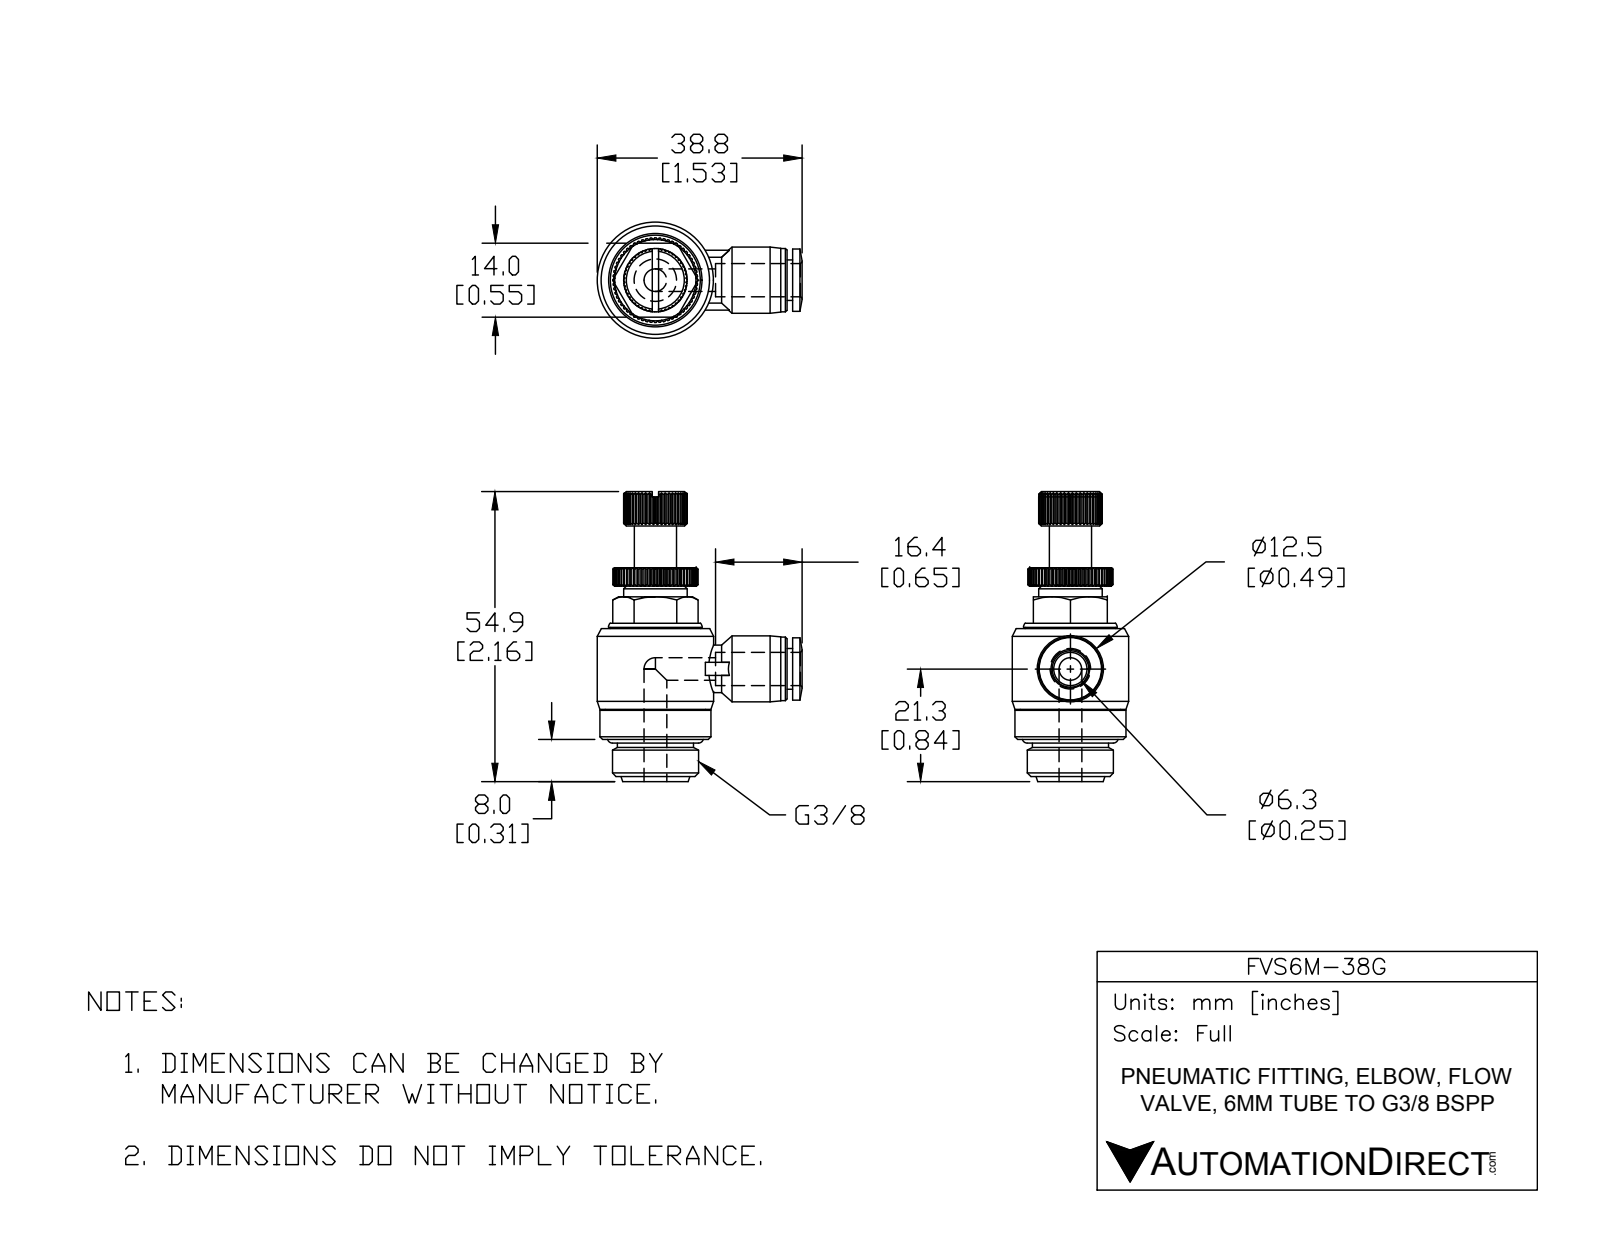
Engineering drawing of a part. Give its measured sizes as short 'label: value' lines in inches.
name: FVS6M-38G
written by: SolidWorks 2015 (AUTOMOTIVE_DESIGN)
unit: in
bodies: 2 solids, 567 faces (251 planar, 143 cylindrical, 173 other)
size: 2.161 × 1.526 × 0.866
volume: 0.802 in³; area: 9.254 in²
holes: 2× ⌀0.169, 1× ⌀0.248
bosses: 2× ⌀0.472, 1× ⌀0.866, 1× ⌀0.827, 1× ⌀0.748, 1× ⌀0.675, 1× ⌀0.642, 1× ⌀0.567, 1× ⌀0.492
rounds: 1× R0.315
face distances: 1.142, 0.315, 0.551, 0.039, 1.594, 1.063, 0.453, 0.276, 0.217, 1.457
